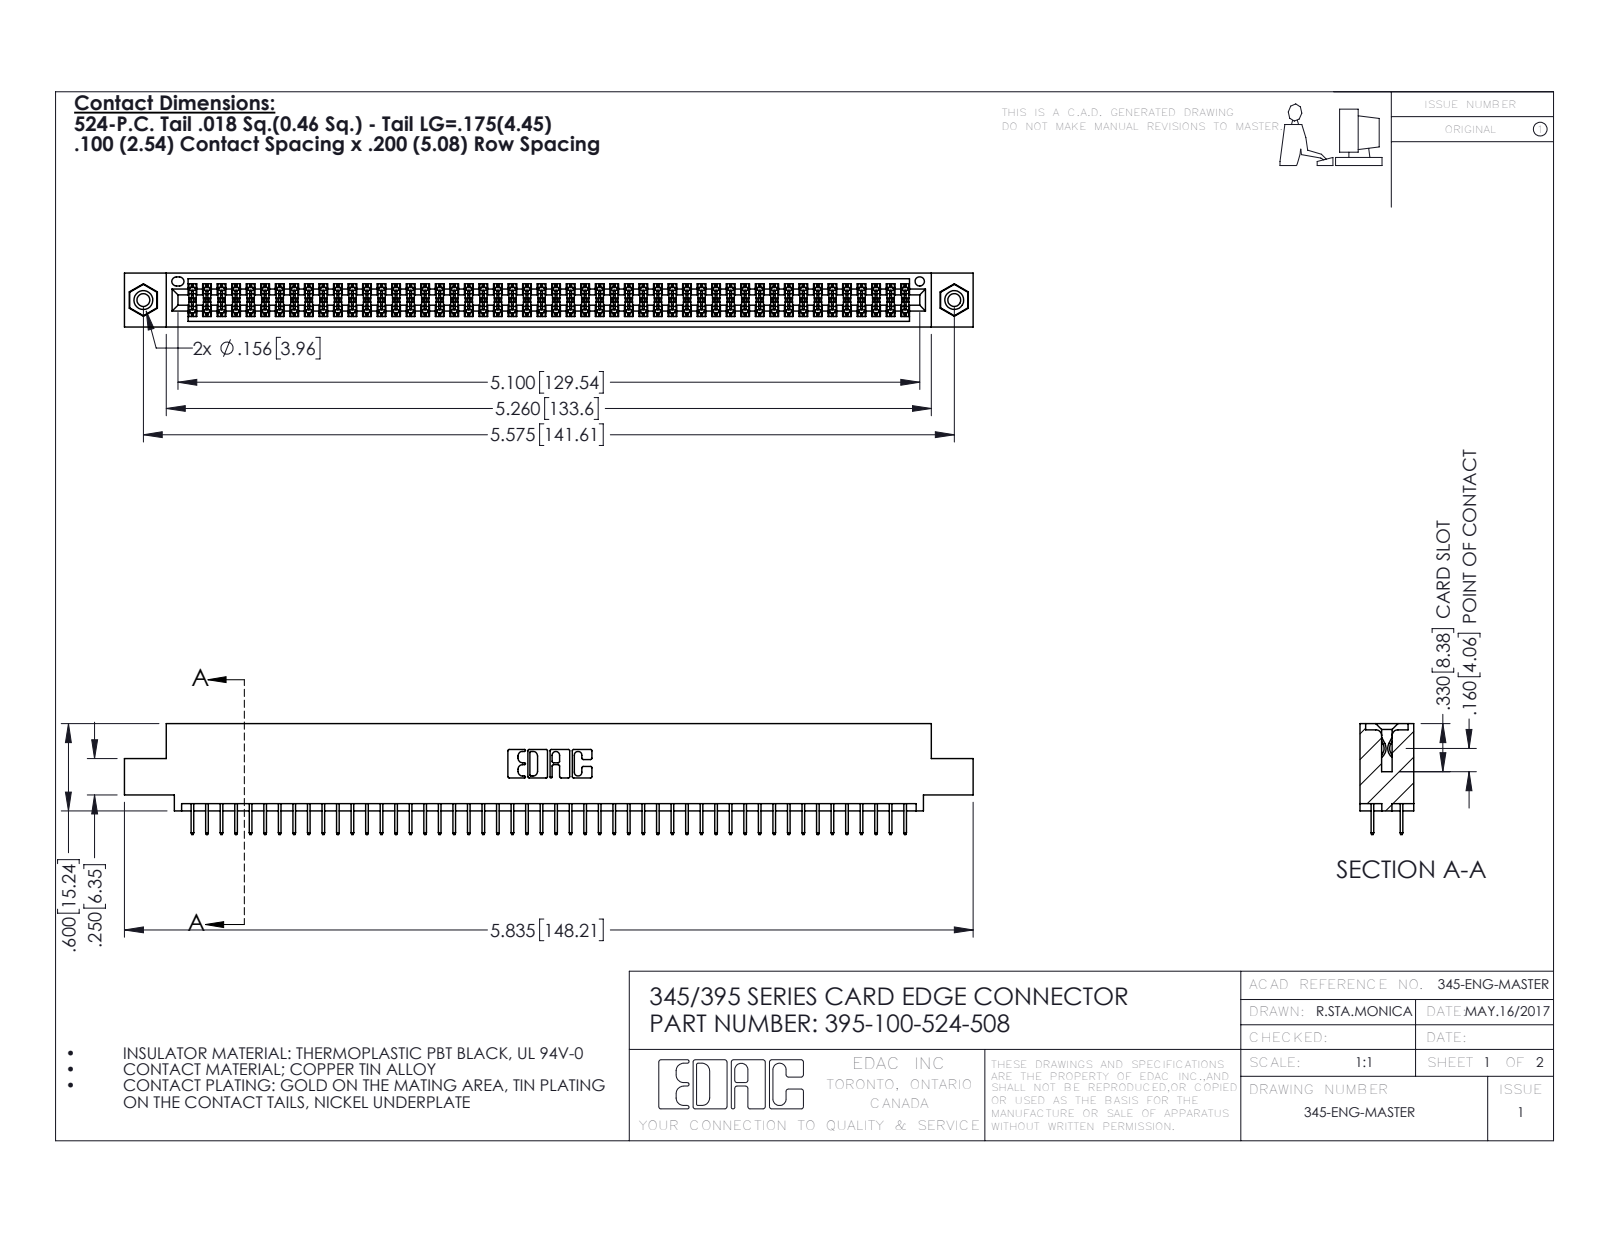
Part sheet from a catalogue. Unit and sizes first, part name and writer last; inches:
Units: inches
Overall size (bounding box): 5.835 × 0.762 × 0.37
Round holes (diameter × count): ⌀0.089 ×2, ⌀0.125 ×2, ⌀0.156 ×2, ⌀0.064 ×1
Round bosses / shafts (diameter × count): ⌀0.155 ×2
Partial cylindrical surfaces — rounded edges, fillets, slot ends (radius × count): R0.006 ×150, R0.01 ×22, R0.007 ×6, R0.031 ×6, R0.026 ×3, R0.014 ×2, R0.019 ×2, R0.022 ×2
Main face-to-face distances: 0.072, 0.298, 0.2, 0.37, 0.098, 0.272, 0.025, 0.225, 0.072, 0.175
Hole centre spacings: 0.27, 5.339, 5.575
Volume: 0.869 in³ · Surface area: 32.41 in²
Bodies: 103 solids, 5590 faces (4016 planar, 1558 cylindrical, 16 other)
Part name (STEP PRODUCT): 395-100-524-508; 345-292-001_345-293-124; 345 Part_0.110 Offset - 0.156 Dia-TI; 345-250-001_345-250-003-102
STEP written by: SolidWorks 2016 (CONFIG_CONTROL_DESIGN)
